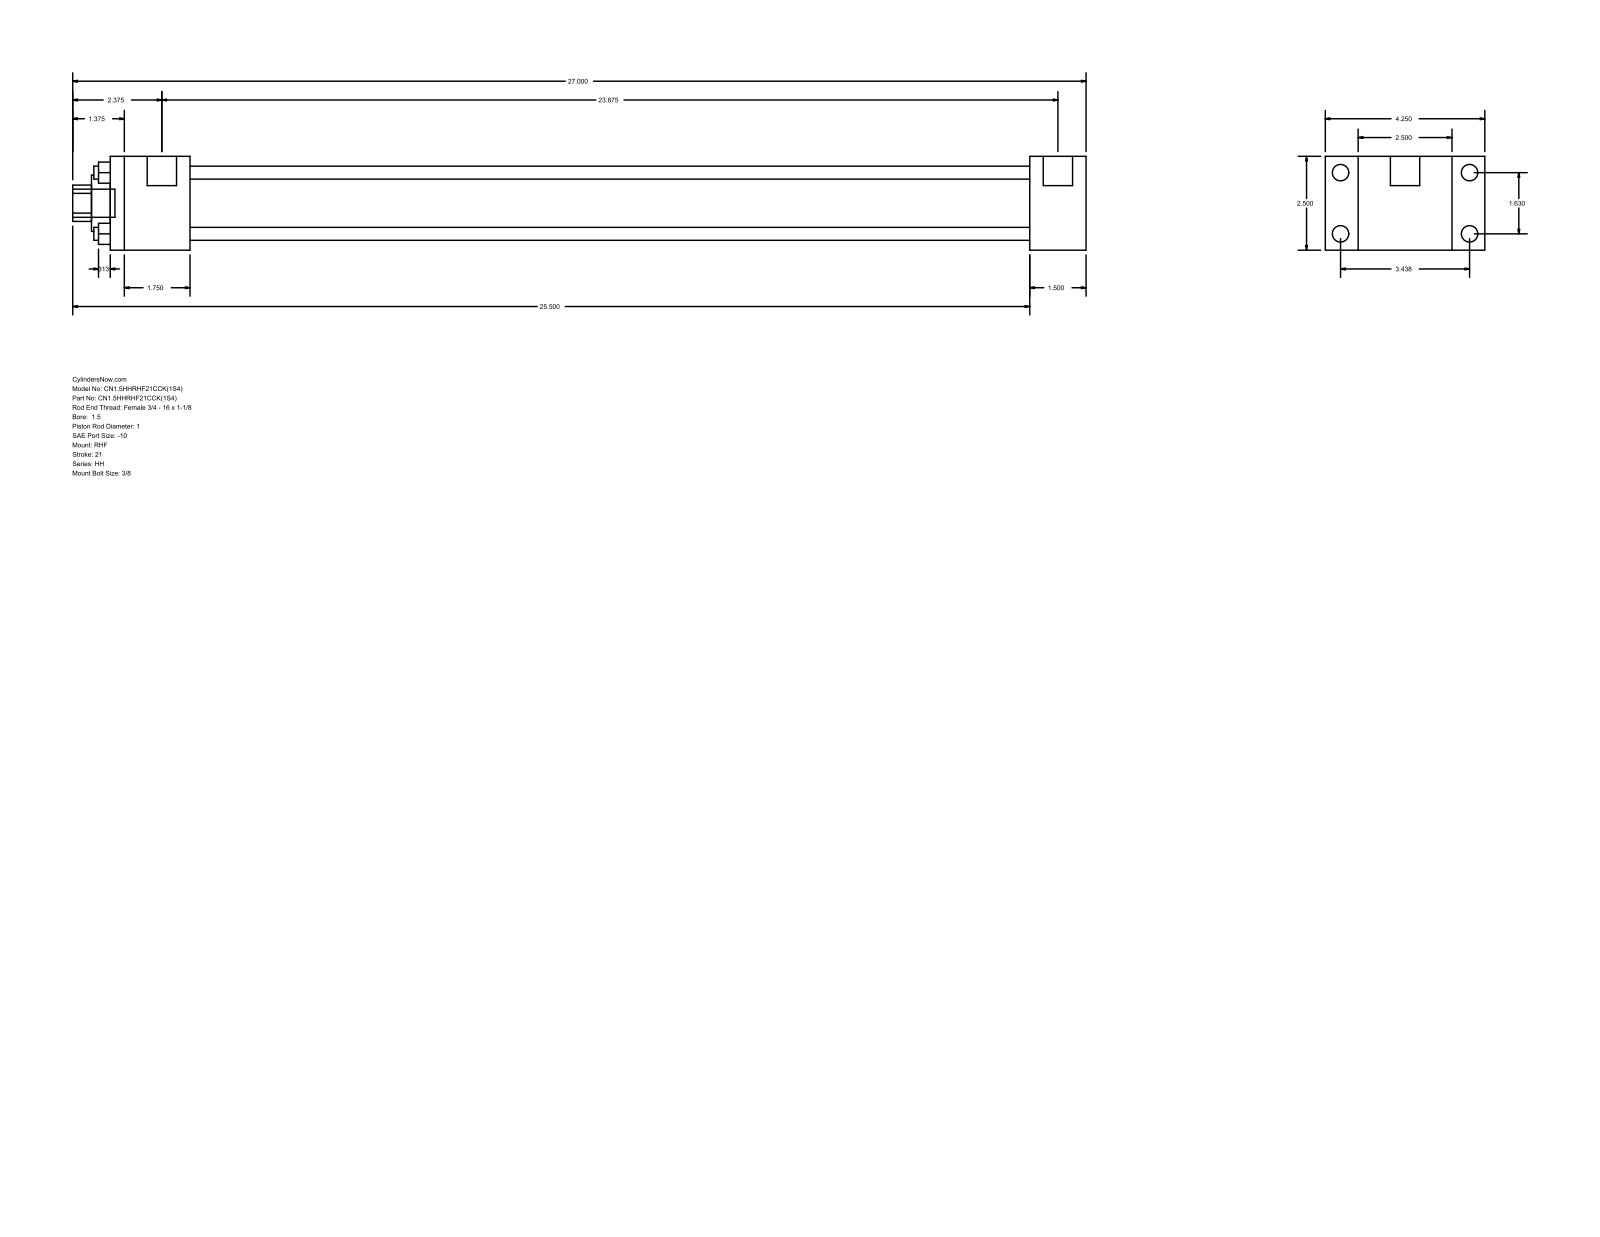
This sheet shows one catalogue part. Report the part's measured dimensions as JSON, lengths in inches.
{"part_name": "HH_RHF__0150_1", "step_written_by": "GSSL Pune (CONFIG_CONTROL_DESIGN)", "units": "inches", "bodies": {"solids": 0, "faces": 88, "planar": 60, "cylindrical": 28, "other": 0}, "overall_size": [27, 4.25, 2.5], "round_holes": [[0.345, 4], [1, 1], [1.5, 1], [1.75, 1]], "round_bosses_or_shafts": [[0.438, 4], [0.219, 4], [0.781, 2], [0.75, 1]], "partial_cylinders_radius": [[0.484, 1]], "face_to_face_distances": [2.5, 0.875, 3.375, 1.5, 4.25, 22.375, 23.875, 2.125, 24.5, 26], "hole_center_spacings": [1.152, 1.63, 2.305]}
